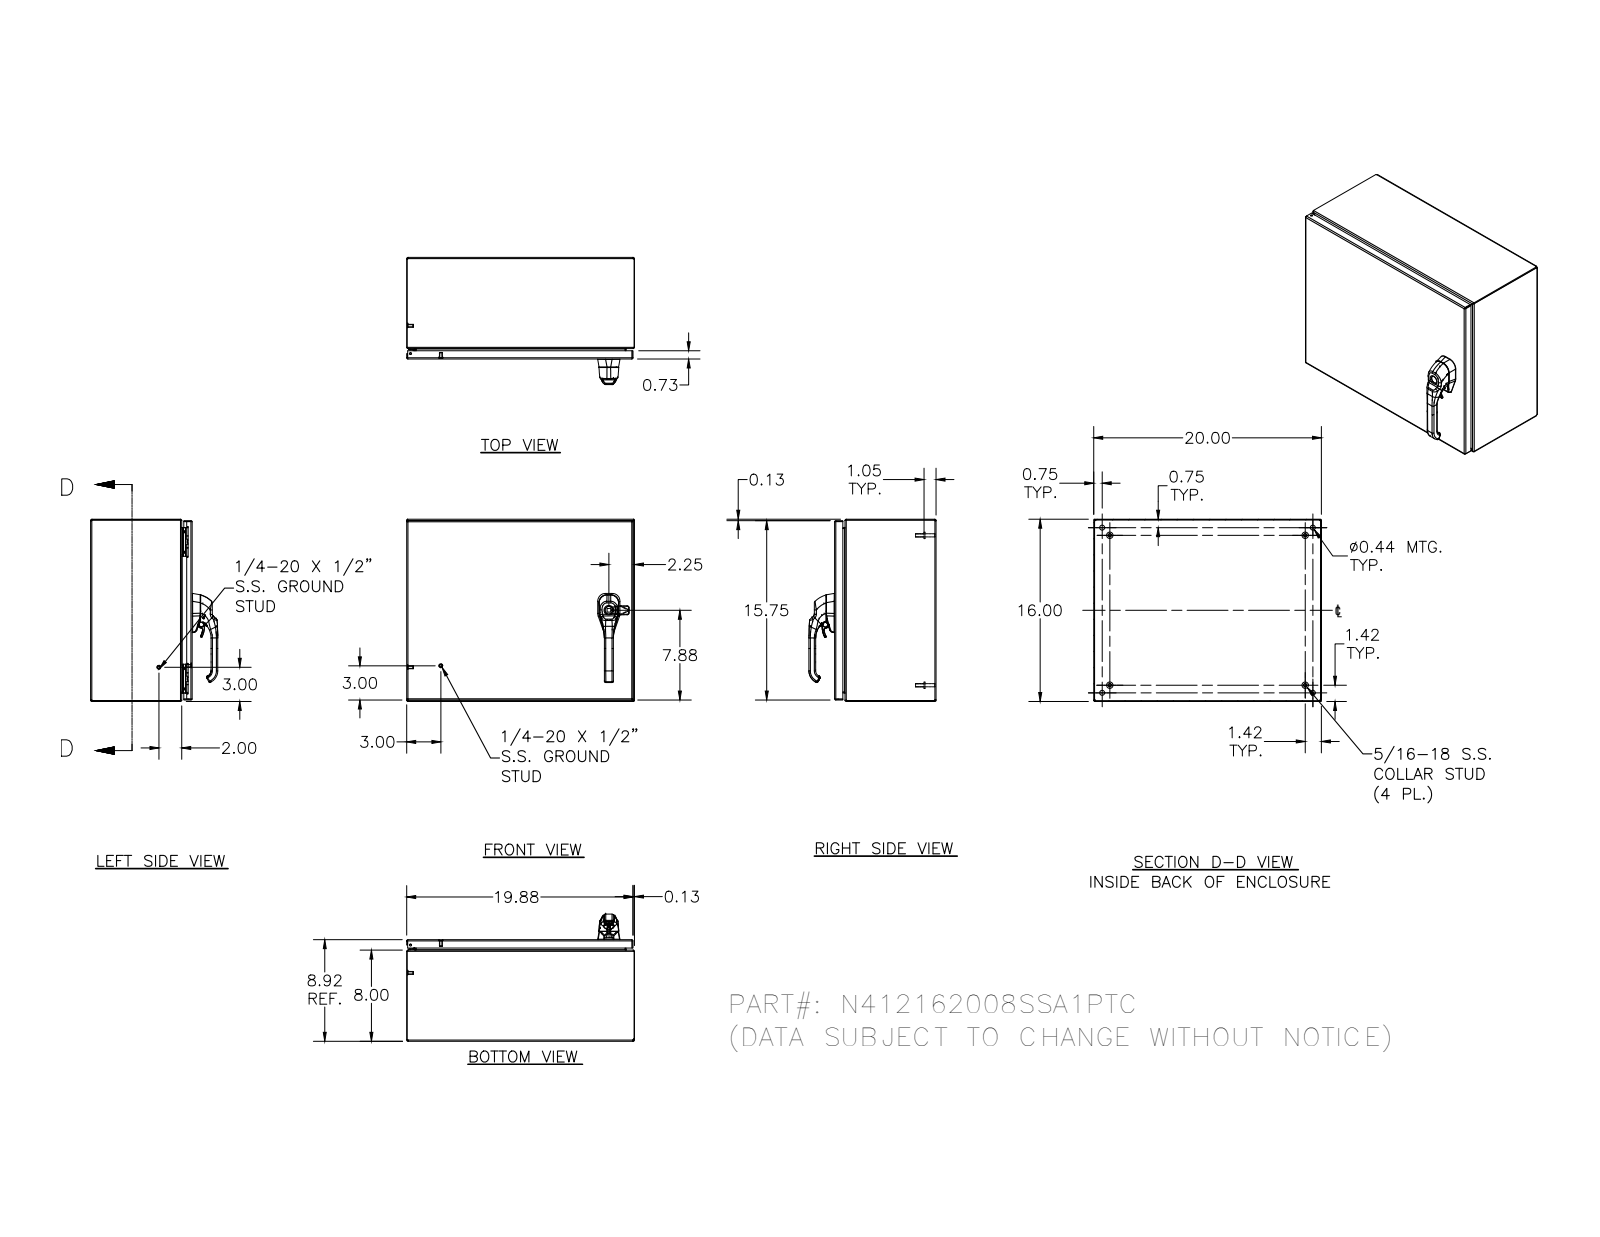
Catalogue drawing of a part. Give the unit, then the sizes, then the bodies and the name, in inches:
Units: inches
Overall size (bounding box): 20 × 16 × 11.166
Round holes (diameter × count): ⌀0.188 ×5, ⌀0.093 ×4, ⌀0.152 ×4, ⌀0.167 ×4, ⌀0.172 ×4, ⌀0.437 ×4, ⌀0.213 ×3, ⌀0.281 ×3, ⌀0.156 ×2, ⌀0.315 ×2, ⌀0.402 ×2, ⌀0.413 ×2
Round bosses / shafts (diameter × count): ⌀0.25 ×10, ⌀0.563 ×4, ⌀0.36 ×4, ⌀0.32 ×4, ⌀0.3 ×4, ⌀0.275 ×4, ⌀0.256 ×4, ⌀0.164 ×4
Partial cylindrical surfaces — rounded edges, fillets, slot ends (radius × count): R0.02 ×173, R0.012 ×101, R0.031 ×30, R0.05 ×26, R0.019 ×21, R0.105 ×20, R0.016 ×18, R0.079 ×14
Main face-to-face distances: 0.074, 8.843, 15.926, 8.917, 8.769, 19.926, 16, 15.852, 19.852, 20
Hole centre spacings: 11.996, 18.872, 0.017, 0.66, 12.656, 17.998, 18.152, 18.183
Volume: 108 in³ · Surface area: 2 837 in²
Bodies: 41 solids, 2784 faces (882 planar, 1037 cylindrical, 865 other)
Part name (STEP PRODUCT): N412162008SSA1PTC; N412162008SSA1PTCBKP; N4121620SSA1PTCLID; HFW328176 (+8 more)
STEP written by: Autodesk Inventor 2012 (AUTOMOTIVE_DESIGN)
